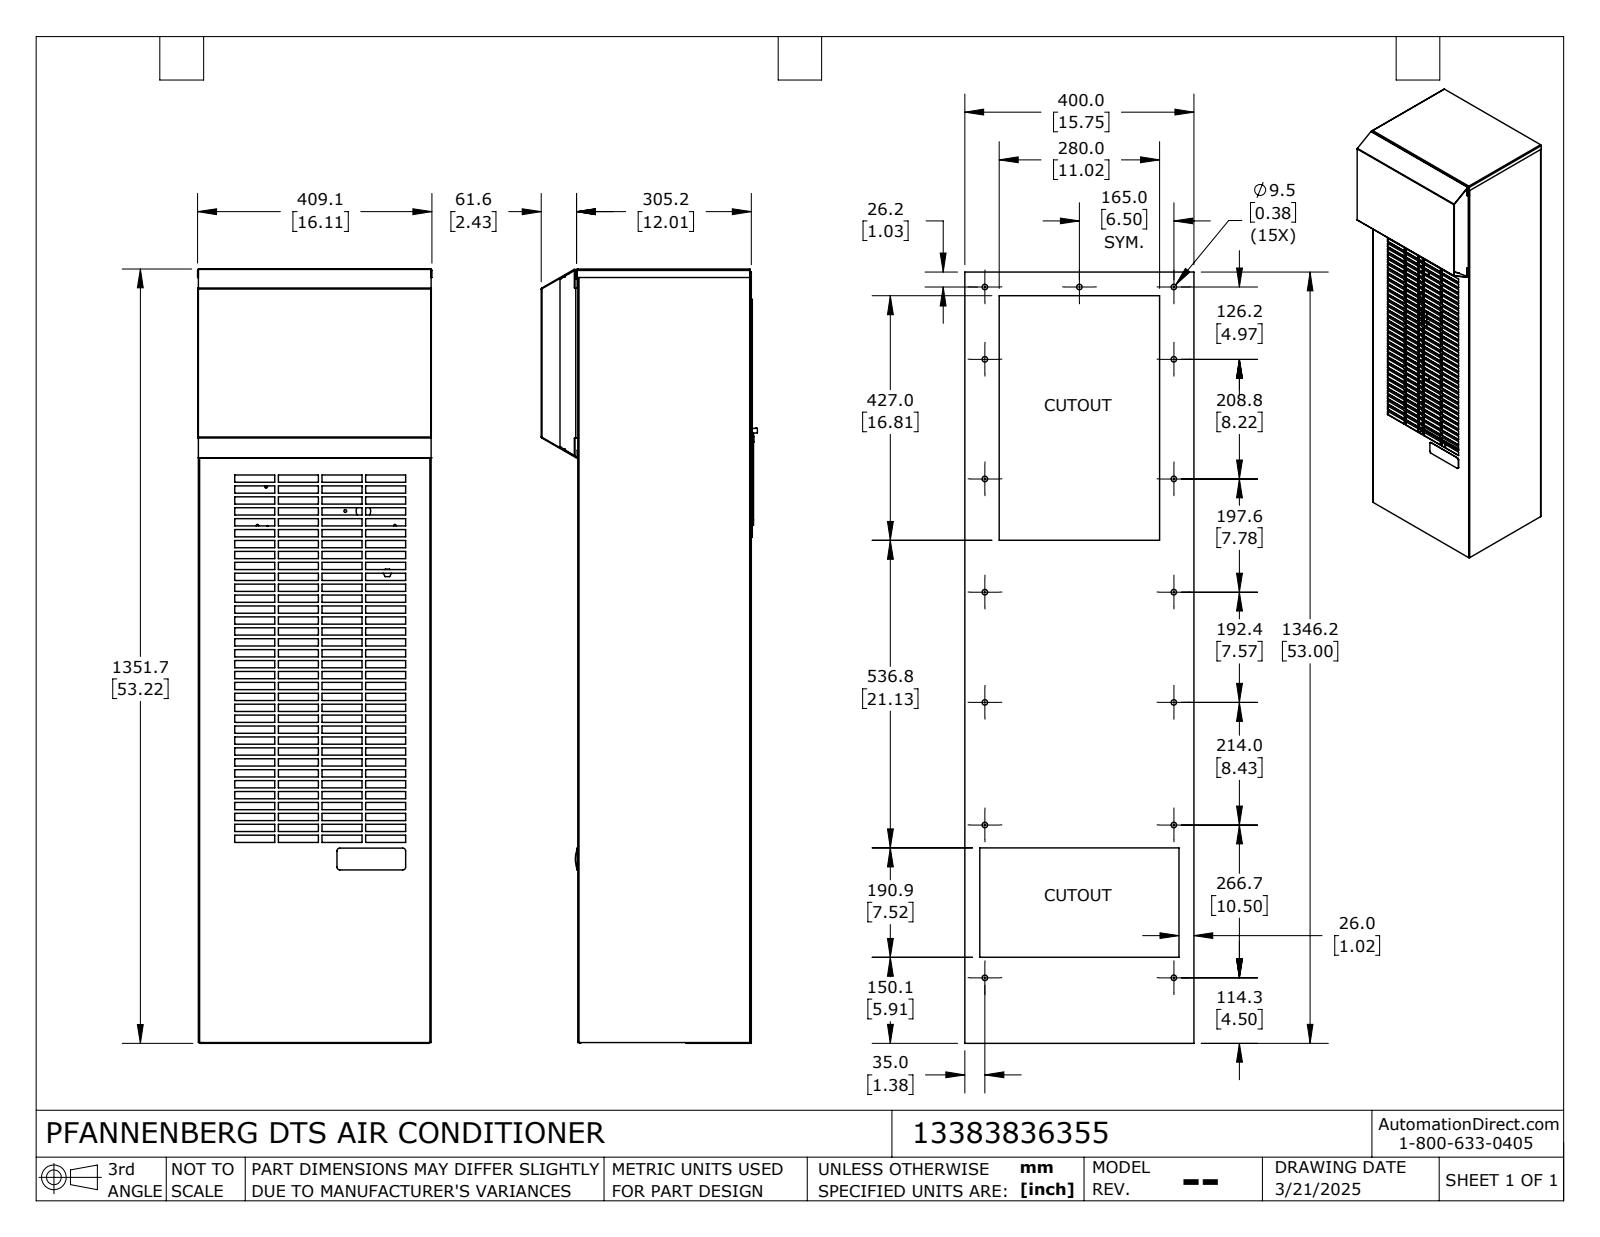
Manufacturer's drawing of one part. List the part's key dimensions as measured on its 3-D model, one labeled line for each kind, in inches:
Part name (STEP PRODUCT): 13383836355_Default
STEP written by: SolidWorks 2024 (CONFIG_CONTROL_DESIGN)
Units: inches
Bodies: 25 solids, 3260 faces (2197 planar, 955 cylindrical, 108 other)
Overall size (bounding box): 53.217 × 16.106 × 14.861
Volume: 474.8 in³ · Surface area: 11 719 in²
Round holes (diameter × count): ⌀0.165 ×72, ⌀0.165 ×18, ⌀0.157 ×15, ⌀0.375 ×15, ⌀0.165 ×10, ⌀0.197 ×8, ⌀0.25 ×8, ⌀0.236 ×7, ⌀0.13 ×5, ⌀0.177 ×4, ⌀0.217 ×4, ⌀0.022 ×2
Round bosses / shafts (diameter × count): ⌀0.079 ×5, ⌀0.276 ×2, ⌀0.031 ×2, ⌀8.858 ×1, ⌀8.78 ×1, ⌀5.866 ×1, ⌀3.622 ×1, ⌀1.063 ×1
Partial cylindrical surfaces — rounded edges, fillets, slot ends (radius × count): R0.125 ×140, R0.031 ×23, R0.079 ×19, R0.03 ×12, R0.078 ×12, R0.031 ×9, R0.079 ×9, R0.197 ×8
Main face-to-face distances: 0.048, 0.048, 15.941, 0.166, 15.99, 15.893, 4.362, 4.528, 11.923, 7.561
Hole centre spacings: 0.02, 15, 4, 4.134, 1.142, 5.846, 8, 8.75
